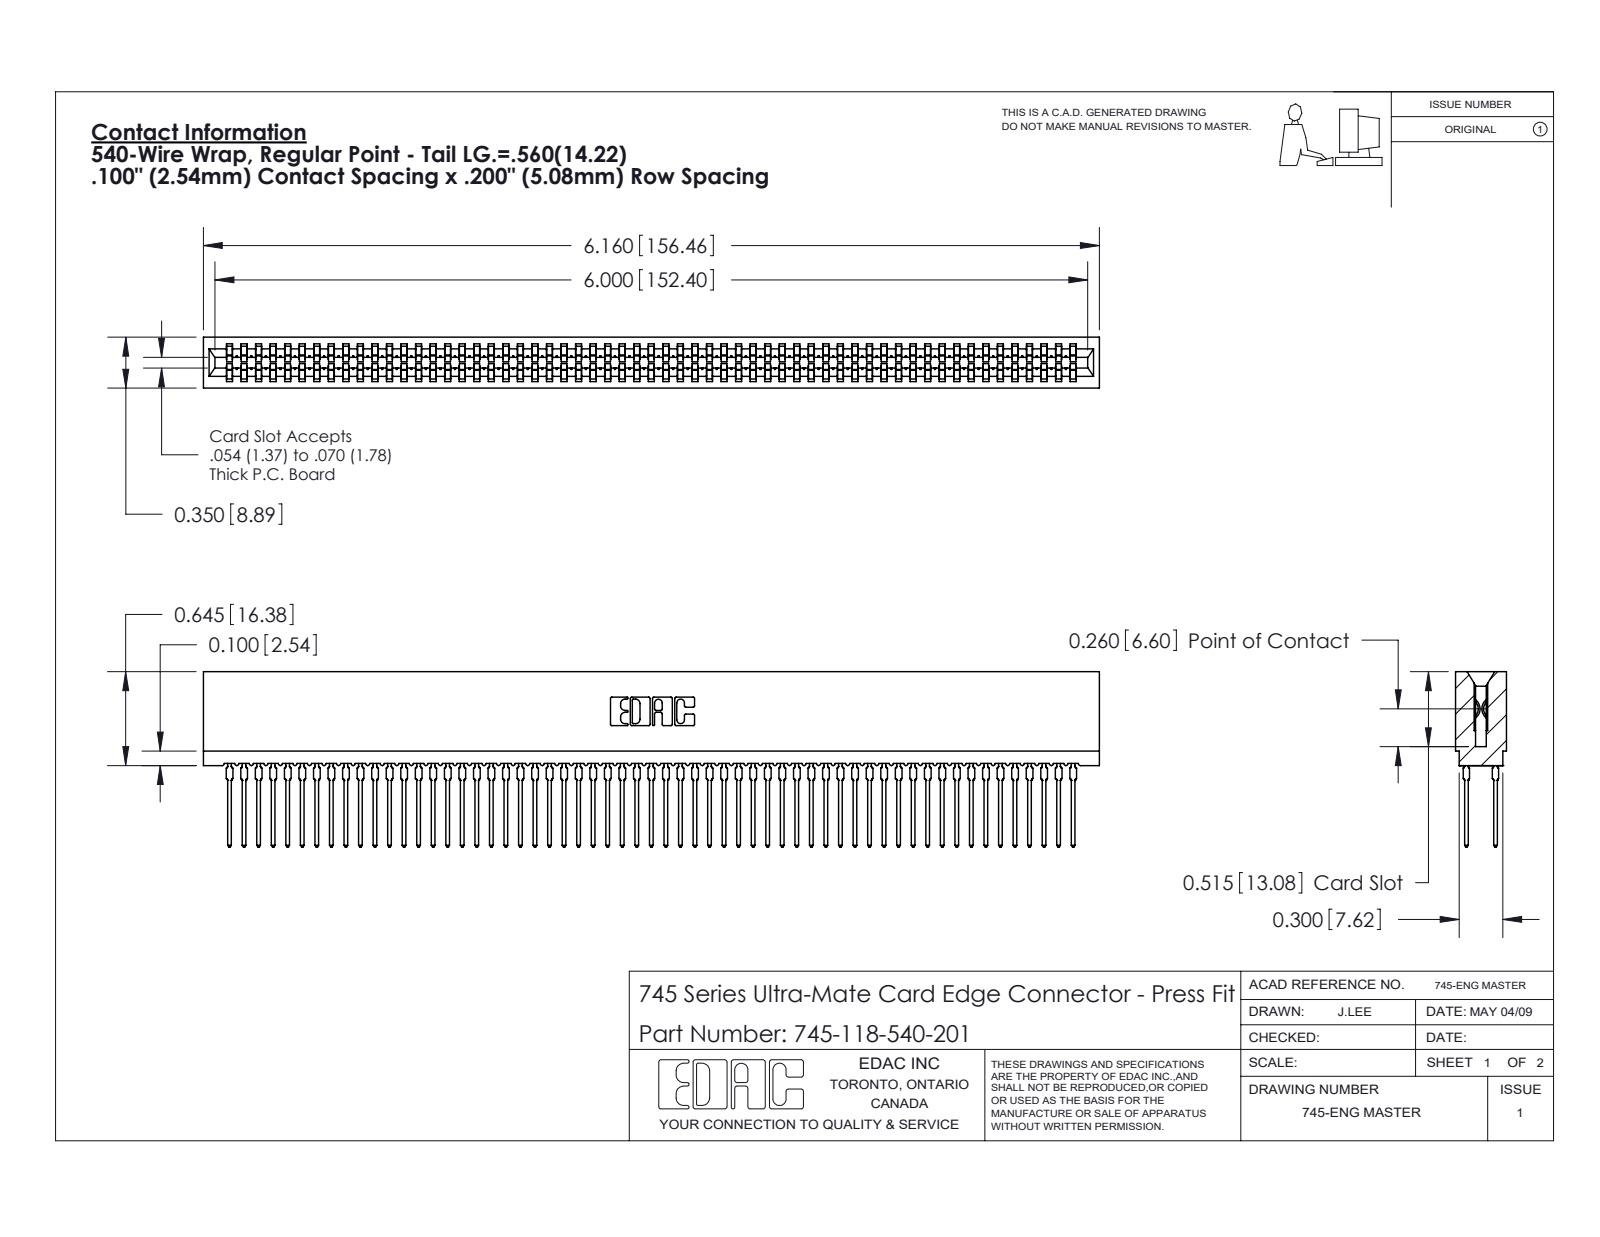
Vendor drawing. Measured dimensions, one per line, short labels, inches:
name: 745-292-001_540; 745 Part_Insulator Option - 01; 745-118-540-201
written by: SolidWorks 2020 (CONFIG_CONTROL_DESIGN)
unit: in
bodies: 119 solids, 10656 faces (5483 planar, 2105 cylindrical, 3068 other)
size: 6.16 × 1.206 × 0.35
volume: 0.875 in³; area: 47.9 in²
rounds: 236× R0.021, 118× R0.015, 22× R0.01, 8× R0.005, 8× R0.011, 6× R0.007, 6× R0.031, 3× R0.026
face distances: 0.063, 0.287, 0.35, 0.2, 0.045, 0.305, 0.018, 0.243, 0.138, 0.212
